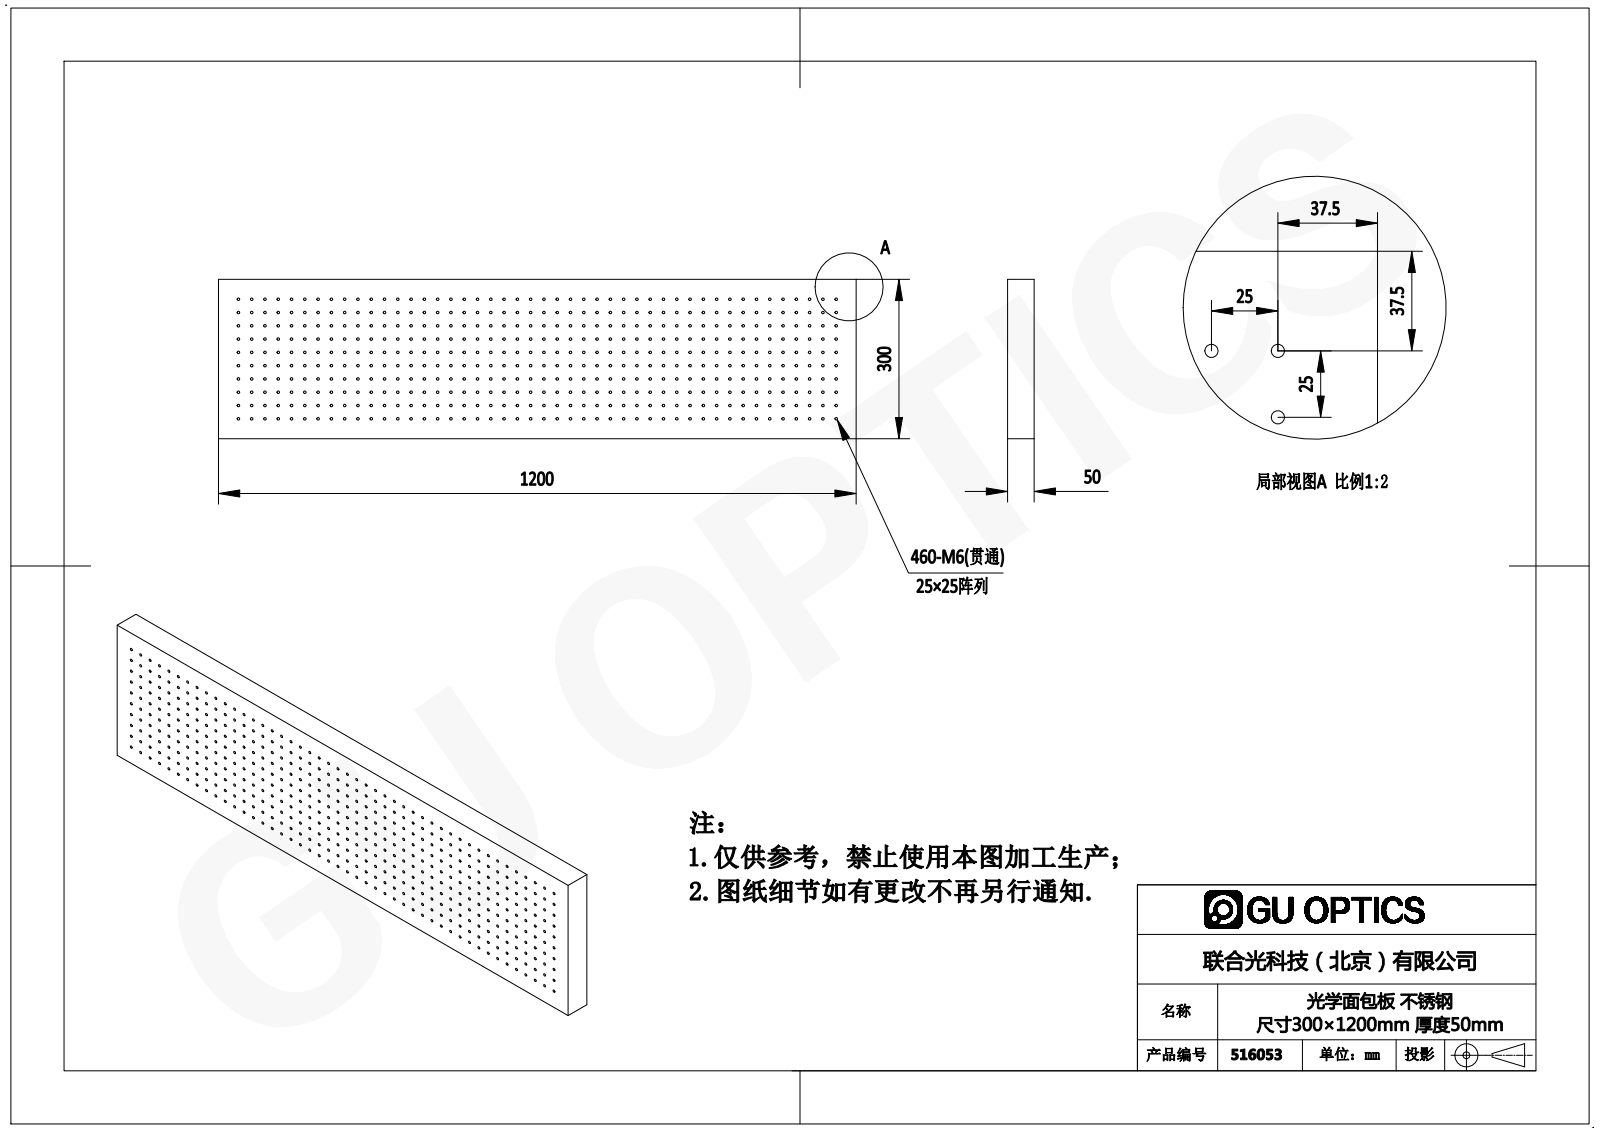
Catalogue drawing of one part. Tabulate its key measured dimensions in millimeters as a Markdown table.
| quantity | value |
| --- | --- |
| part name | 516053 |
| STEP written by | SolidWorks 2016 (AUTOMOTIVE_DESIGN) |
| units | millimeters |
| bodies | 1 solid, 926 faces (6 planar, 920 cylindrical, 0 other) |
| overall size | 1200 × 300 × 50 |
| volume | 17 550 000 mm³ |
| surface area | 1 213 000 mm² |
| round holes (diameter × count) | 5 × 460 |
| main face-to-face distances | 50, 300, 1200 |
| hole center spacings | 55.9, 25, 35.36, 79.06, 50, 90.14, 103.08, 75 |
